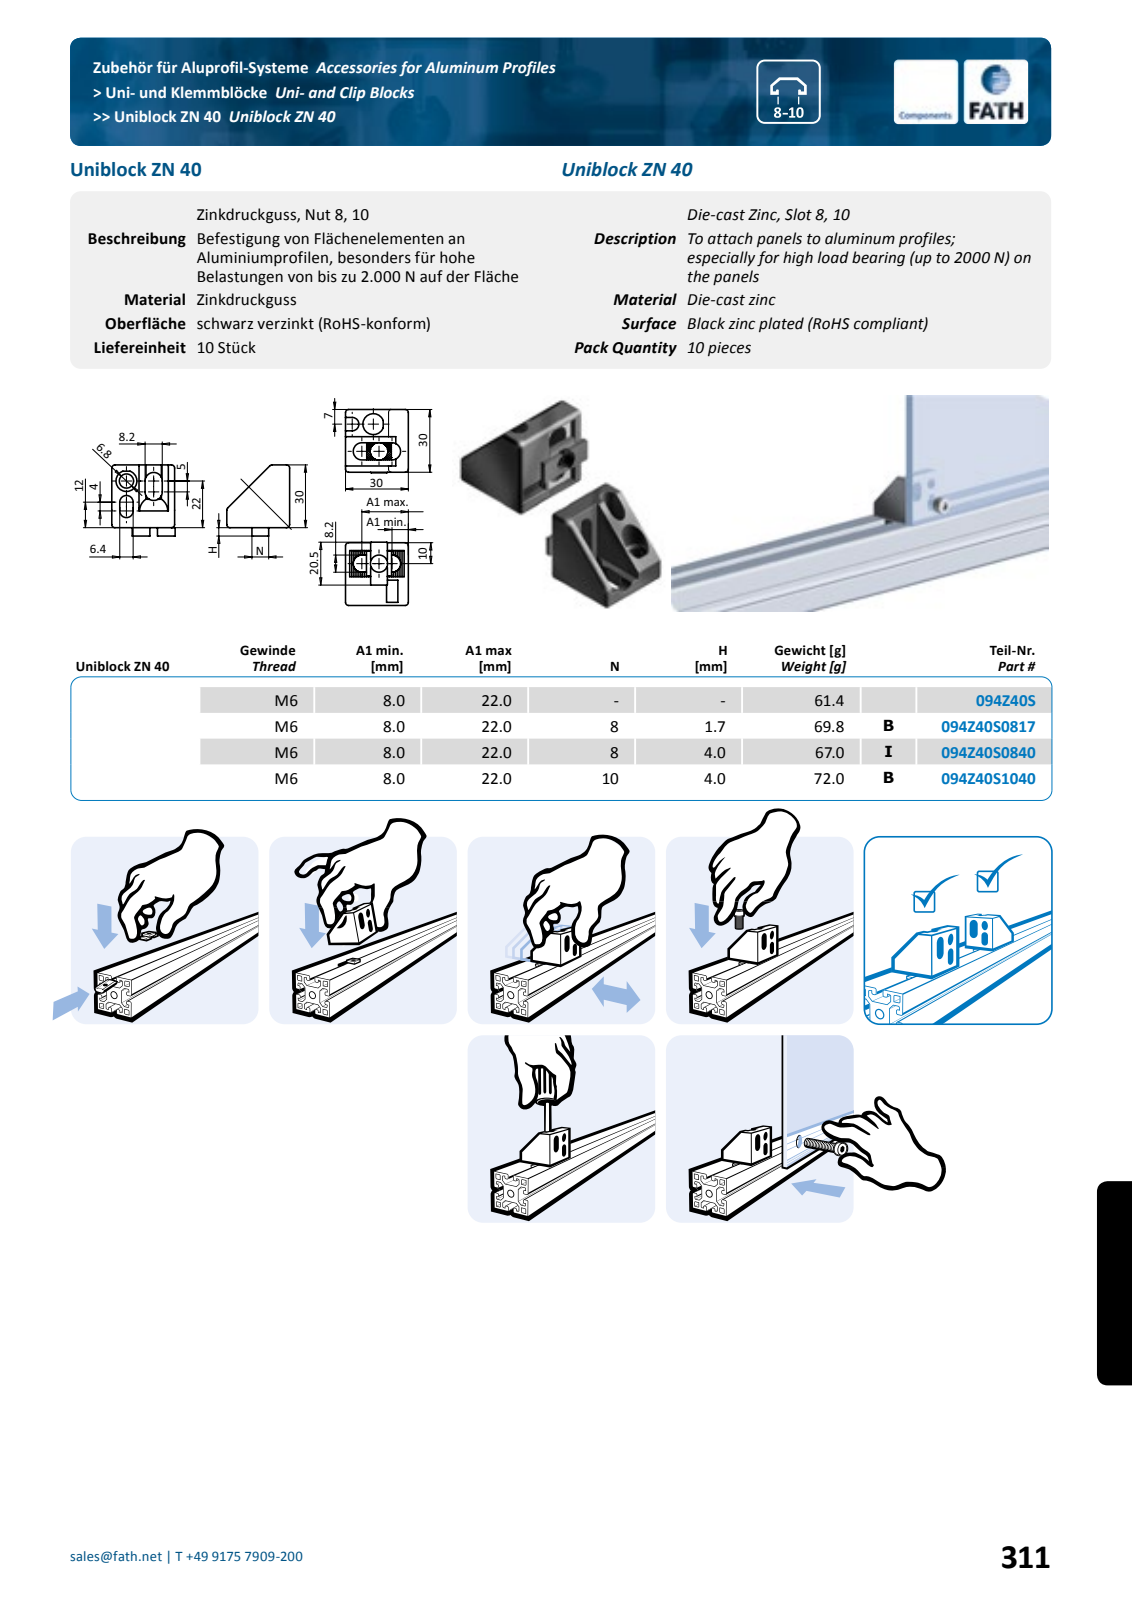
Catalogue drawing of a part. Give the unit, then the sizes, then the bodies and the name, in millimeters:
Units: millimetres
Overall size (bounding box): 30 × 30 × 30
Round holes (diameter × count): ⌀6.8 ×1, ⌀10 ×1
Partial cylindrical surfaces — rounded edges, fillets, slot ends (radius × count): R0.2 ×21, R1.5 ×15, R0.3 ×4, R4.1 ×4, R2 ×2, R3.2 ×2, R6.25 ×2, R7.25 ×1
Main face-to-face distances: 30, 27.25, 2.75, 12.75, 14.5, 17.25, 0.7, 11.35, 3.15, 8
Volume: 9 864 mm³ · Surface area: 6 660 mm²
Bodies: 1 solid, 258 faces (135 planar, 68 cylindrical, 55 other)
Part name (STEP PRODUCT): fath_094z40s0840
STEP written by: Spatial InterOp 3D (automotive_design)
